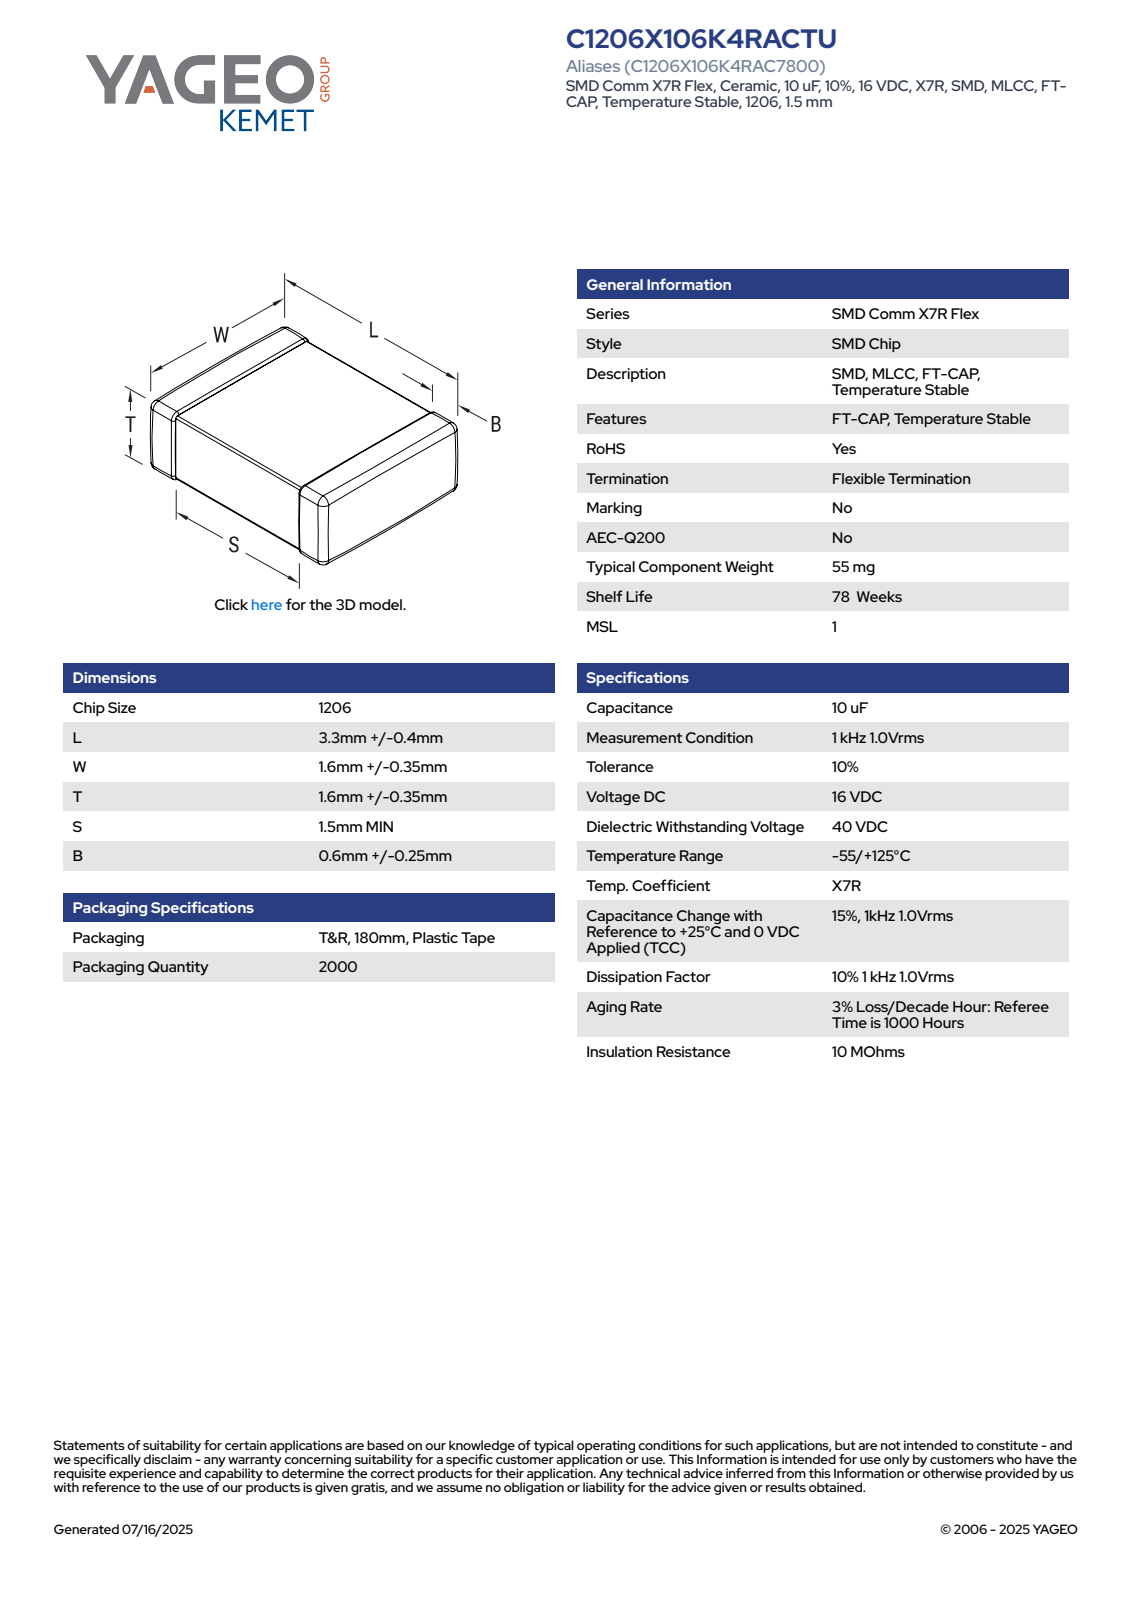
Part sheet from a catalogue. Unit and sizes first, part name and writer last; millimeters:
Units: millimetres
Overall size (bounding box): 3.7 × 1.95 × 1.95
Main face-to-face distances: 1.91, 1.87, 1.95, 3.7, 1.71, 1.99, 2, 1.7, 0.78, 0.52
Volume: 13 mm³ · Surface area: 36 mm²
Bodies: 4 solids, 129 faces (71 planar, 42 cylindrical, 16 other)
Part name (STEP PRODUCT): CCS_CCSTD_1206_L3.7W1.95T1.95B0.6
STEP written by: SolidWorks 2021 (AUTOMOTIVE_DESIGN)
